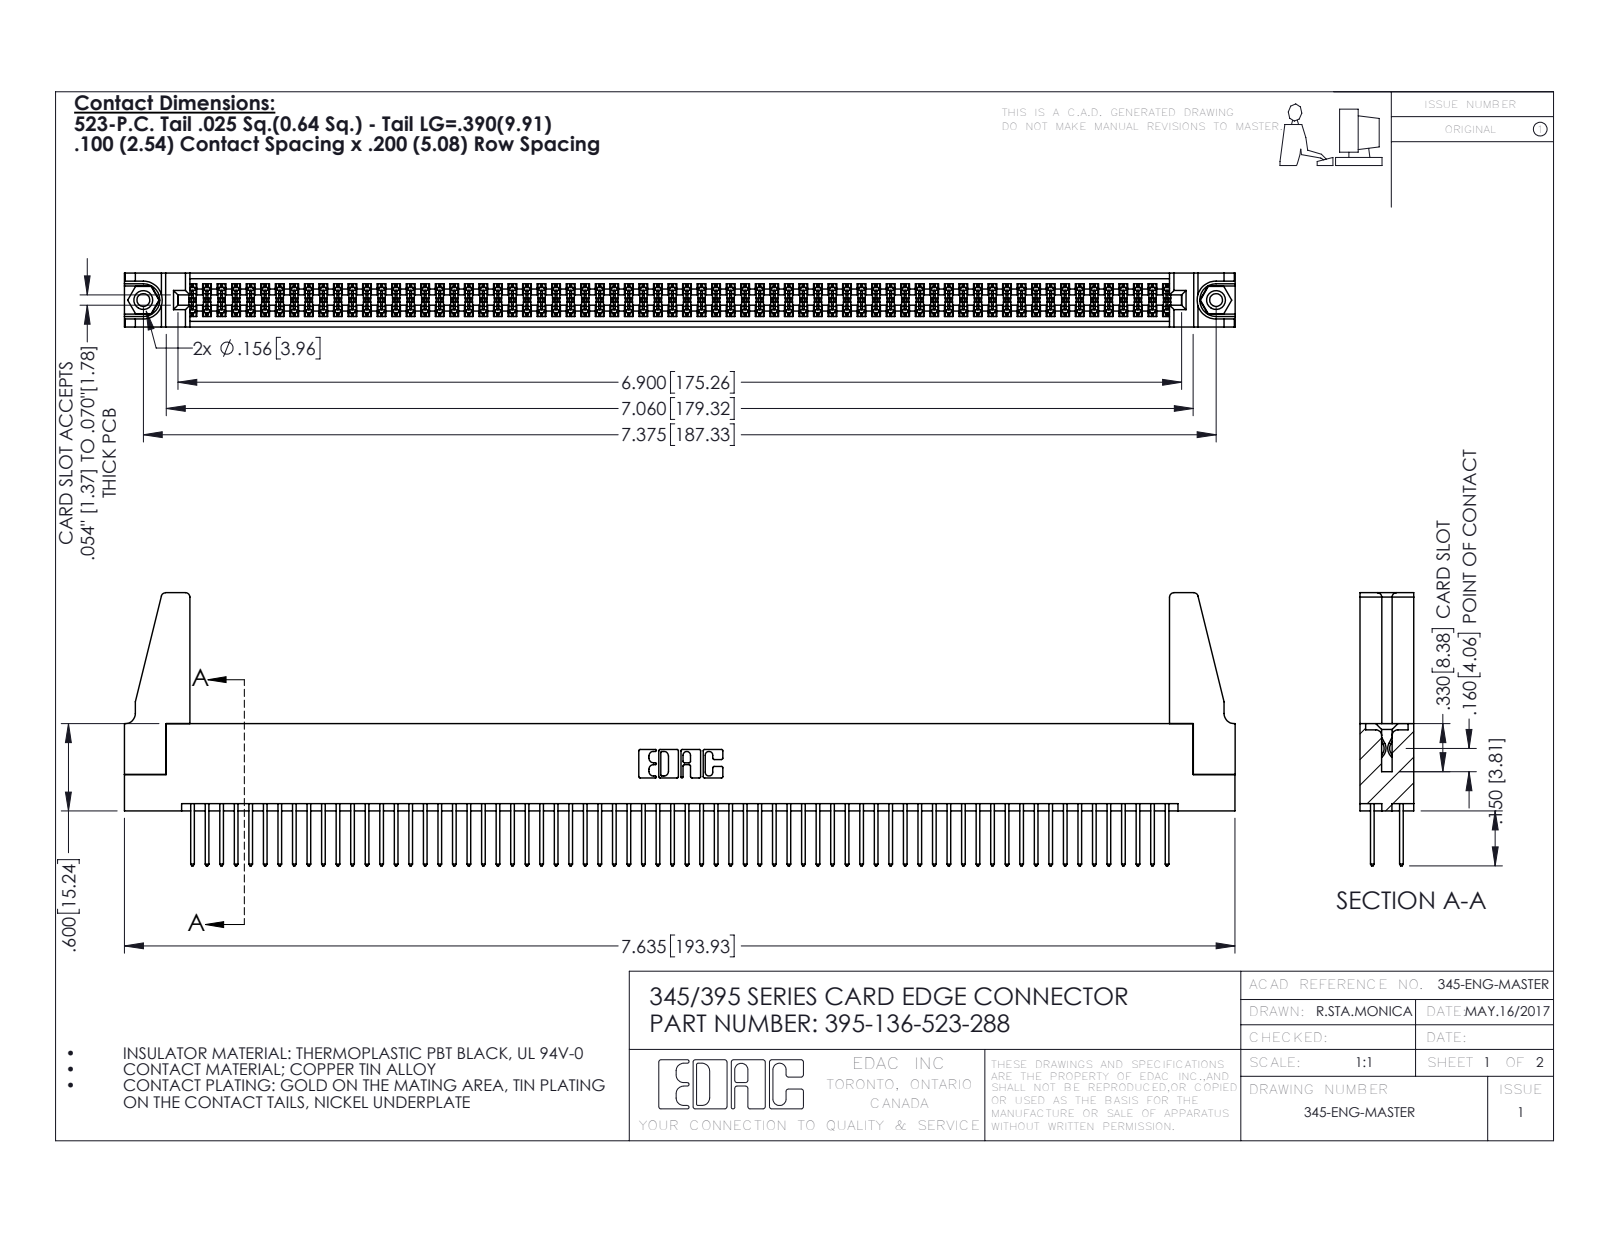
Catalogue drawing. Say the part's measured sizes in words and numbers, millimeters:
The part is named "345-292-001_345-293-123; 345 Part_Flush Mounting Lugs - 0.156 Dia-TH; 395-136-523-288; 345-220-078_345-220-088 (+1 more)". Its 3-D file was written by "SolidWorks 2016 (CONFIG_CONTROL_DESIGN)". It is 141 solids with 7050 faces: 4640 planar, 2394 cylindrical and 16 other. Overall it measures 194 by 47.7 by 9.4 millimeters. Its volume is 22 610 cubic millimeters and its surface area 33 500 square millimeters. Round holes: 2 of diameter 2.3, 2 of diameter 3.2, 2 of diameter 4, 1 of diameter 1.6. Round bosses or shafts: 2 of diameter 3.9. Partial cylindrical surfaces (rounded edges, fillets, slot ends): 204 of radius 0.2, 136 of radius 0.3, 22 of radius 0.3, 8 of radius 0.8, 6 of radius 0.2, 6 of radius 0.8, 3 of radius 0.7, 2 of radius 0.4. The main face-to-face distances are 1.8, 7.6, 5.1, 2.5, 6.9, 0.6, 9.4, 5.7, 4.4, 3.8. The hole center spacings are 6.9, 181.3, 187.3.
